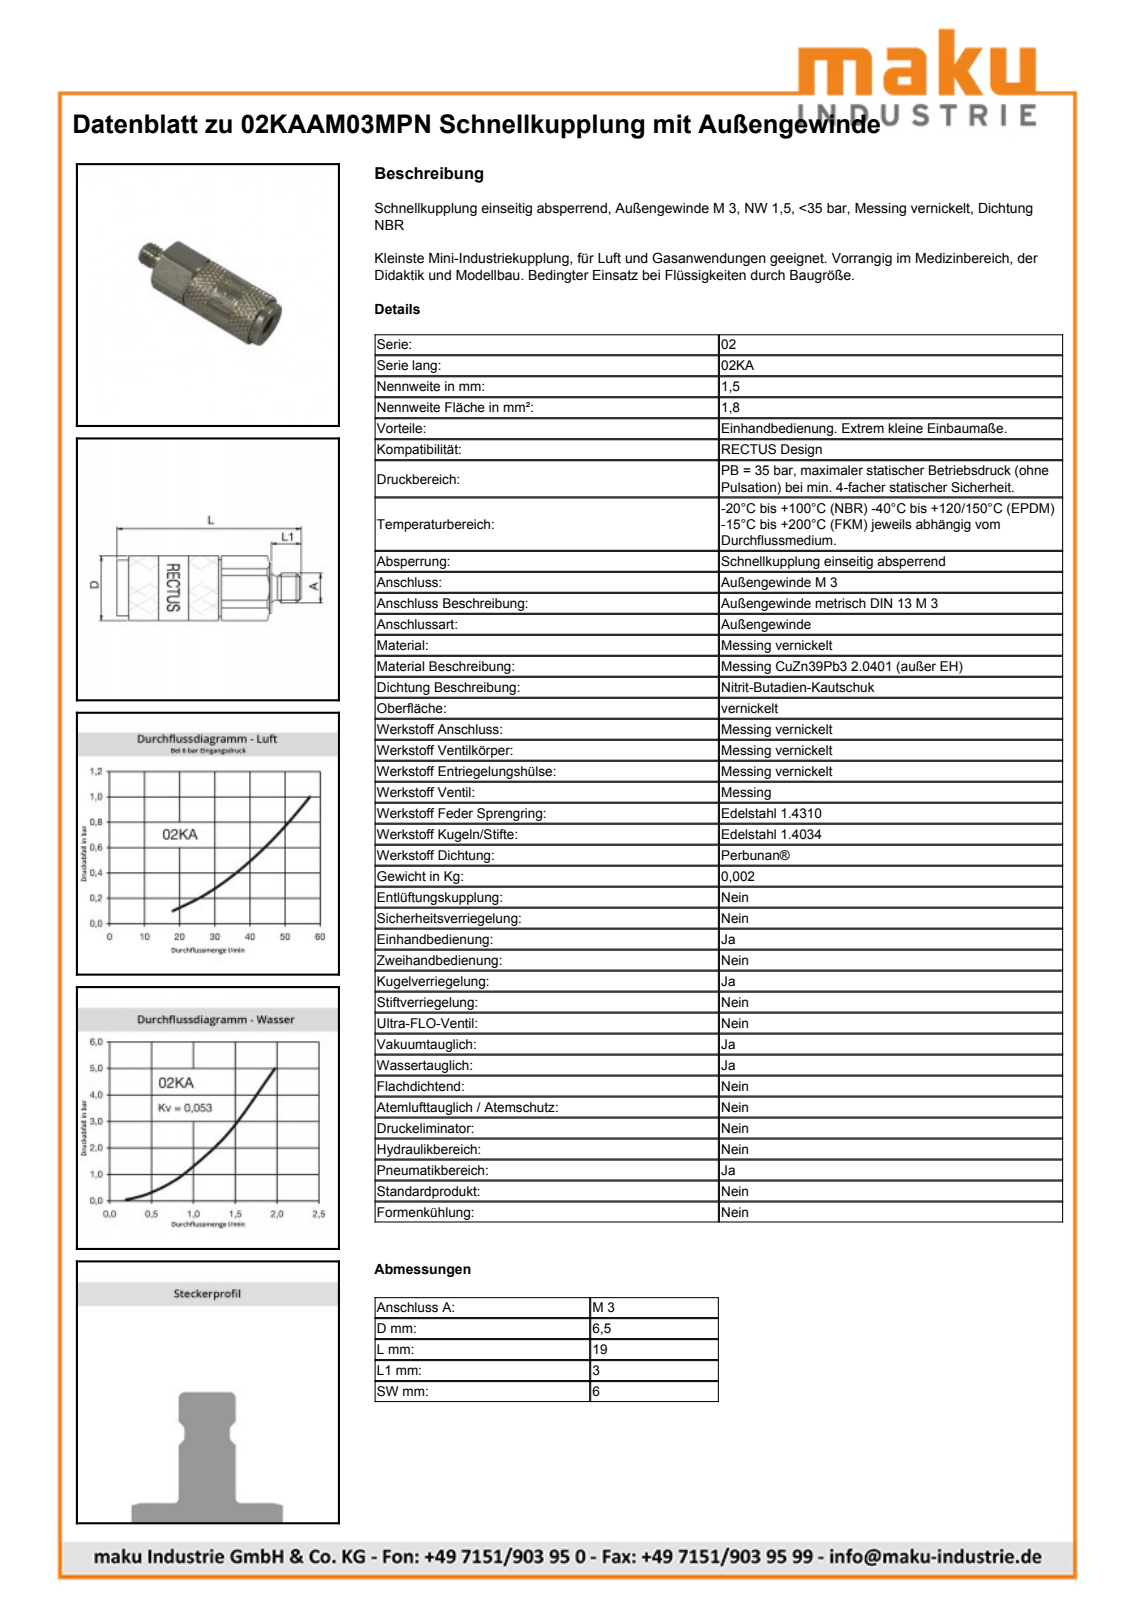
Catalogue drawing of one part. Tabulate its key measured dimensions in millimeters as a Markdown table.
| quantity | value |
| --- | --- |
| part name | D109641 |
| STEP written by | Autodesk Inventor 2013 (AUTOMOTIVE_DESIGN) |
| units | millimeters |
| bodies | 2 solids, 261 faces (87 planar, 44 cylindrical, 130 other) |
| overall size | 18.5 × 6.5 × 6.5 |
| volume | 443 mm³ |
| surface area | 804 mm² |
| round holes (diameter × count) | 4.5 × 1, 5.15 × 1, 5.75 × 1, 5.8 × 1 |
| round bosses / shafts (diameter × count) | 6.5 × 1, 6.3 × 1, 5.7 × 1, 5.6 × 1, 5 × 1, 4.4 × 1, 4.25 × 1, 3 × 1 |
| partial cylindrical surfaces (radius × count) | 1.96 × 1, 3.05 × 1 |
| main face-to-face distances | 6, 15.5, 2.5, 14.35, 3, 15.3, 1.15, 14.15, 10.15, 9 |
